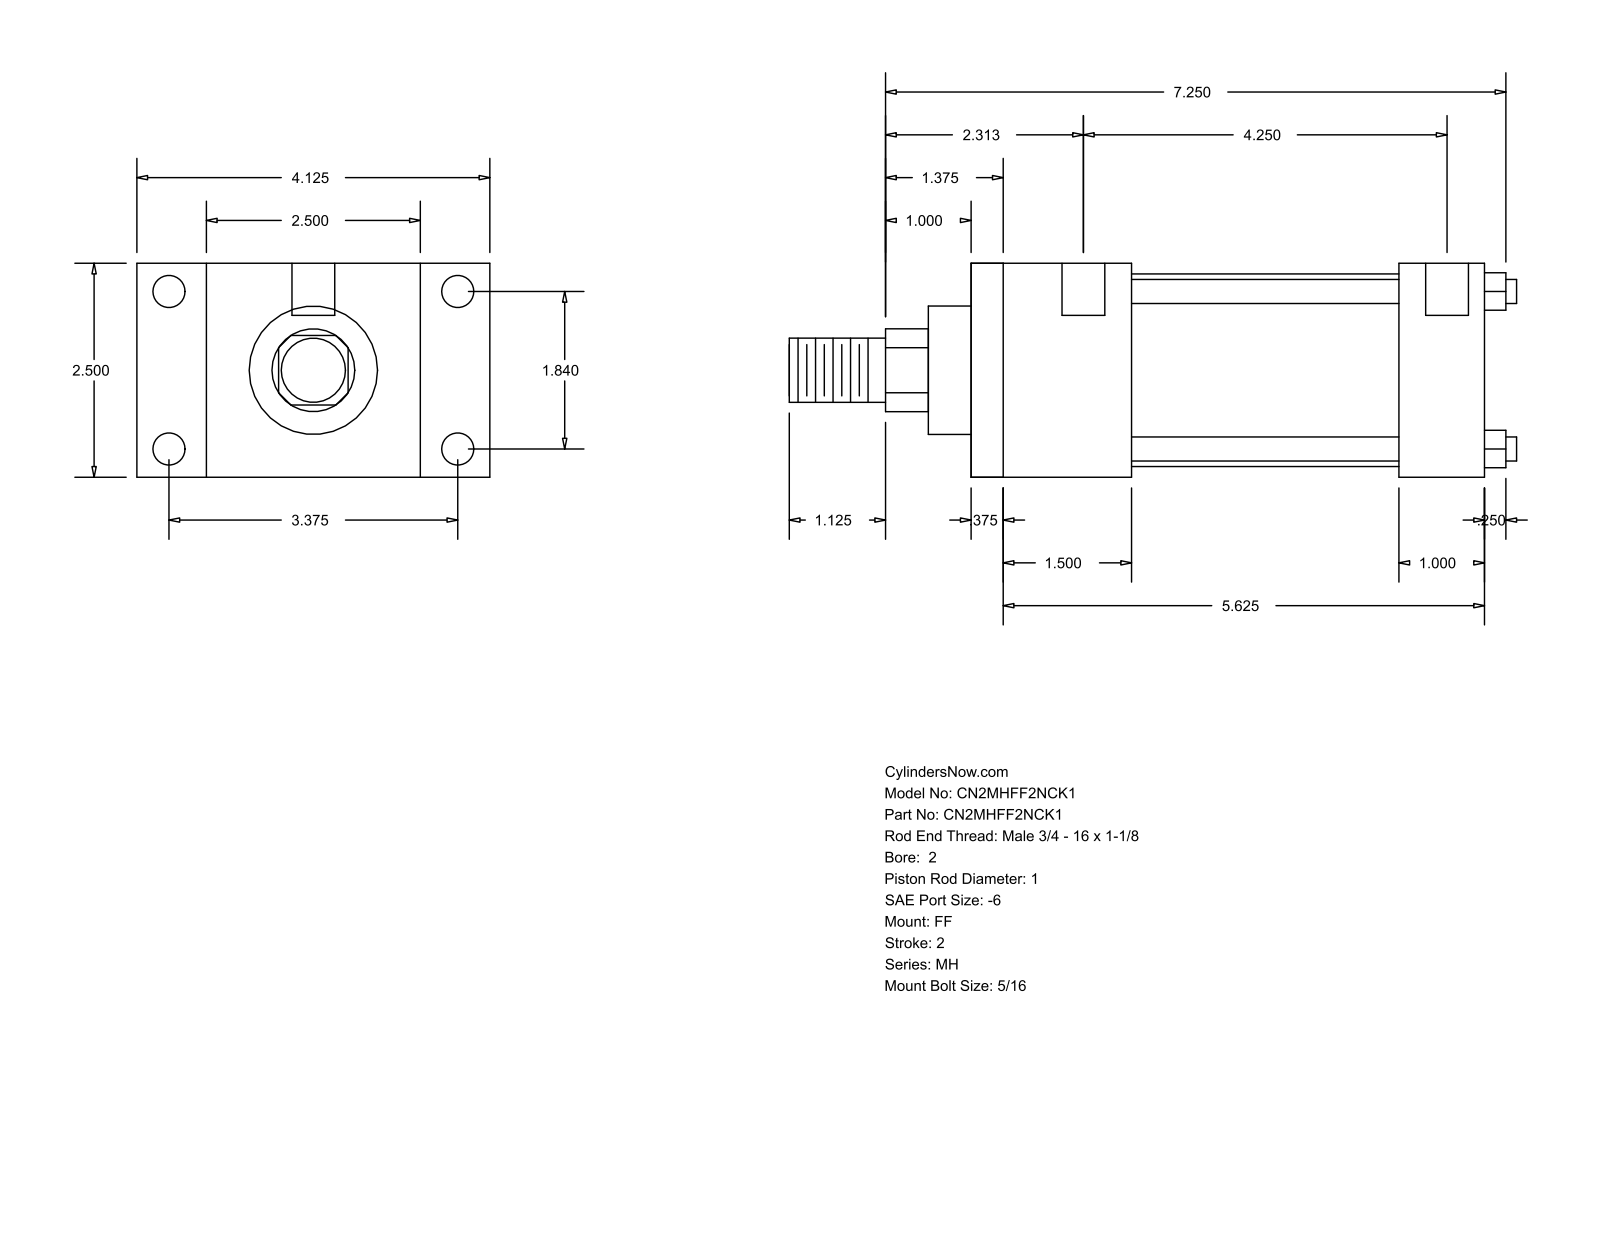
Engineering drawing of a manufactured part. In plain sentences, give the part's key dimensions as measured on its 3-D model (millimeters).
The part is named "MH_FF__0200_1". Its 3-D file was written by "GSSL Pune (CONFIG_CONTROL_DESIGN)". It is 0 solids with 92 faces: 64 planar, 28 cylindrical and 0 other. Overall it measures 215.9 by 104.78 by 63.5 millimeters. Round holes: 4 of diameter 5.56, 4 of diameter 9.53, 2 of diameter 12.7. Round bosses or shafts: 4 of diameter 7.14, 1 of diameter 57.15, 1 of diameter 38.1, 1 of diameter 25.4, 1 of diameter 19.05. Partial cylindrical surfaces (rounded edges, fillets, slot ends): 1 of radius 12.29. The main face-to-face distances are 63.5, 152.4, 9.52, 142.88, 20.64, 25.4, 47.63, 127, 38.11, 117.48. The hole center spacings are 46.74, 85.72, 97.63, 115.88, 3.17, 4.76, 107.95, 111.12.
